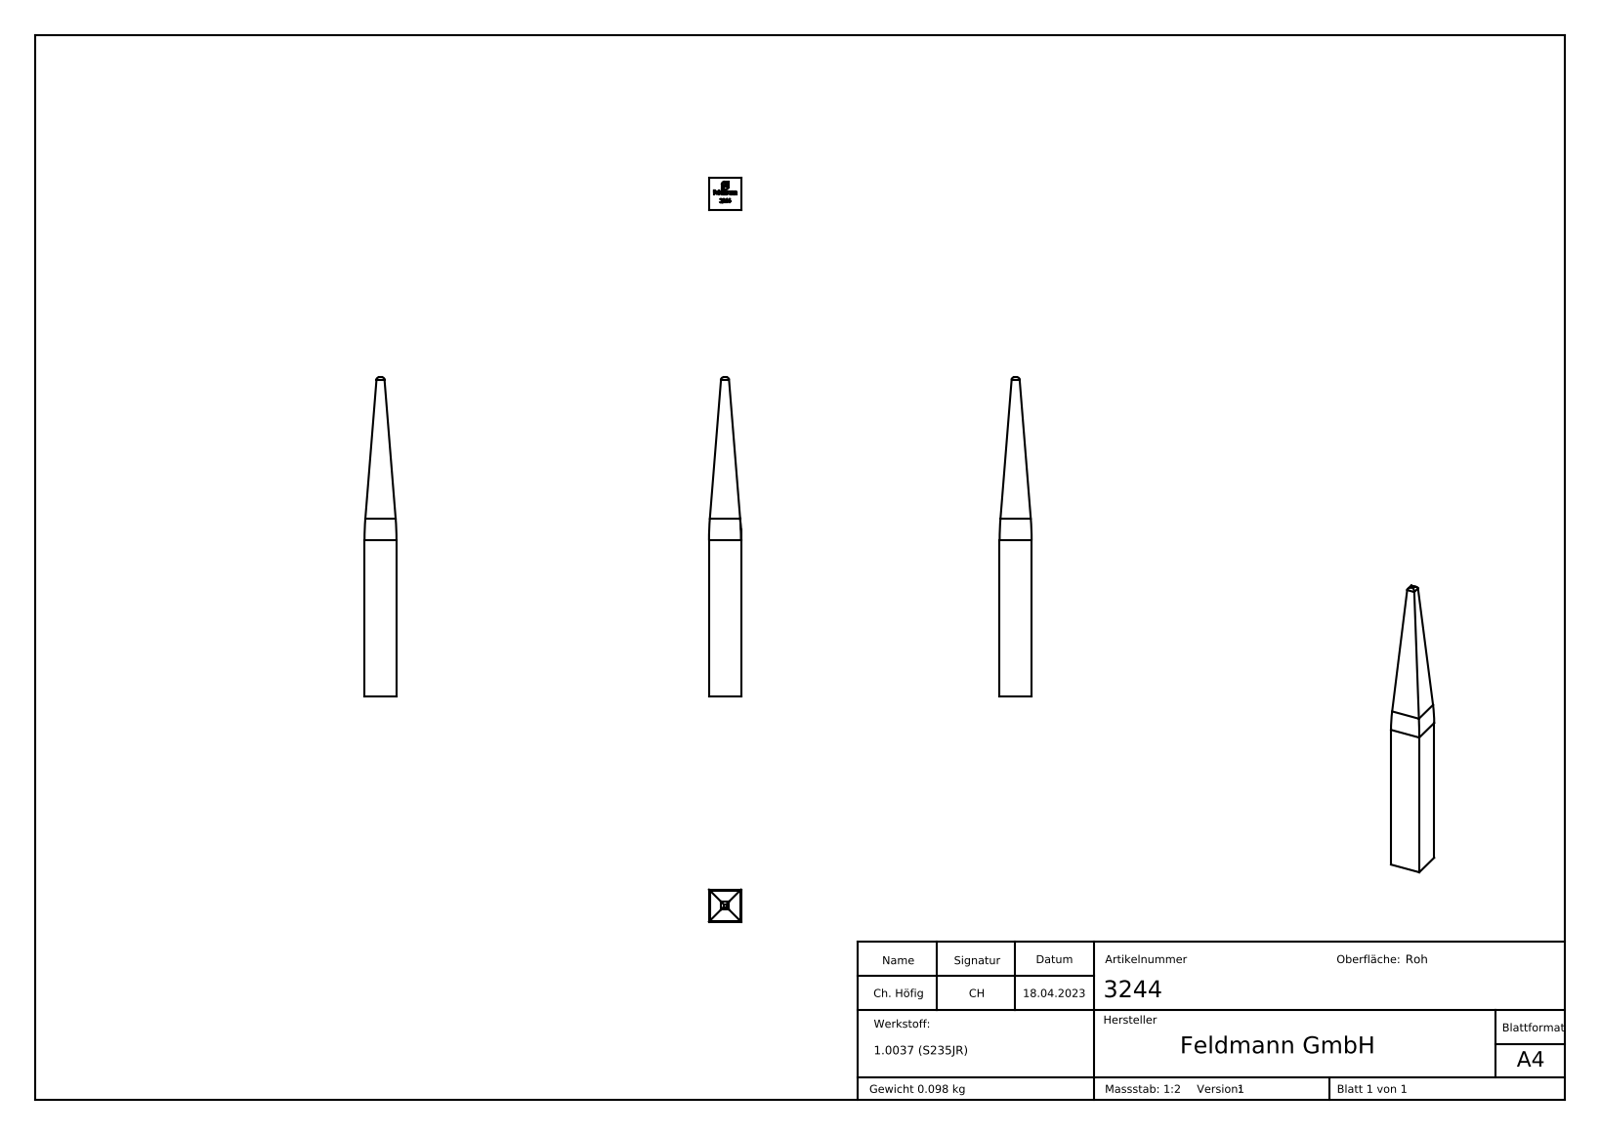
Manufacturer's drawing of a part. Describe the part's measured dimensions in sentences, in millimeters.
The part is named "3244". Its 3-D file was written by "SolidWorks 2018 (CONFIG_CONTROL_DESIGN)". It is 1 solid with 235 faces: 139 planar, 8 cylindrical and 88 other. Overall it measures 120 by 12 by 12 millimeters. Its volume is 12 599 cubic millimeters and its surface area 4 878 square millimeters. Partial cylindrical surfaces (rounded edges, fillets, slot ends): 4 of radius 1, 4 of radius 100. The main face-to-face distances are 12, 120, 119.9, 2.9, 3.1, 3.36, 3.85, 0.34, 6, 1.01.
